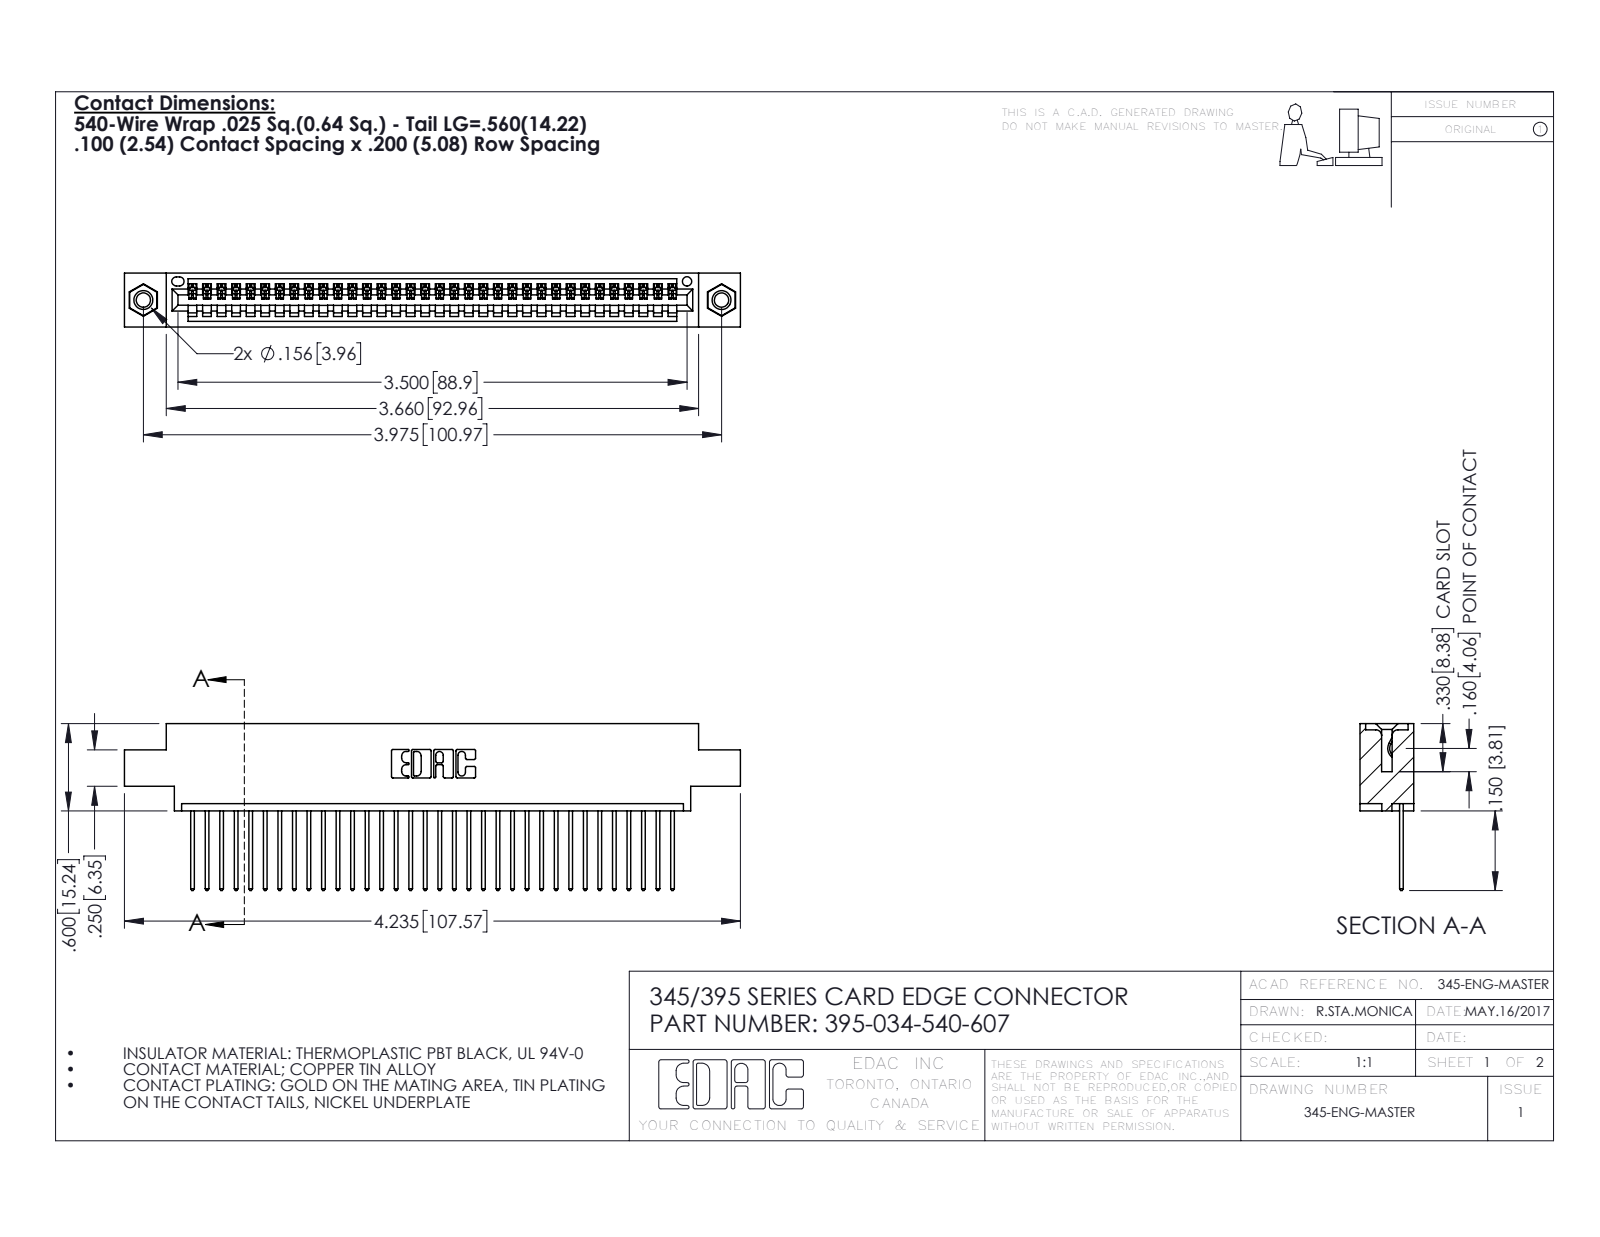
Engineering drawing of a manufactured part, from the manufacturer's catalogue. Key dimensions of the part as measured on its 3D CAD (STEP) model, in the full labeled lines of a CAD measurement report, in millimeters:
Part name (STEP PRODUCT): 345 Part_0.170 Offset - 0.156 Dia-TI; 395-034-540-607; 345-250-001_345-250-005-103; 345-292-001_345-293-140
STEP written by: SolidWorks 2016 (CONFIG_CONTROL_DESIGN)
Units: millimetres
Bodies: 37 solids, 2162 faces (1476 planar, 670 cylindrical, 16 other)
Overall size (bounding box): 107.6 × 29.1 × 9.4
Volume: 10 100 mm³ · Surface area: 13 770 mm²
Round holes (diameter × count): ⌀2.5 ×2, ⌀3.2 ×2, ⌀4 ×2, ⌀1.6 ×1
Round bosses / shafts (diameter × count): ⌀3.9 ×2
Partial cylindrical surfaces — rounded edges, fillets, slot ends (radius × count): R0.2 ×68, R0.3 ×68, R0.3 ×22, R0.2 ×6, R0.8 ×6, R0.7 ×3, R0.8 ×2, R1 ×2
Main face-to-face distances: 1.8, 7.6, 9.4, 2.5, 6.9, 0.6, 5.1, 5.7, 4.4, 3.8
Hole centre spacings: 6.9, 95, 101
